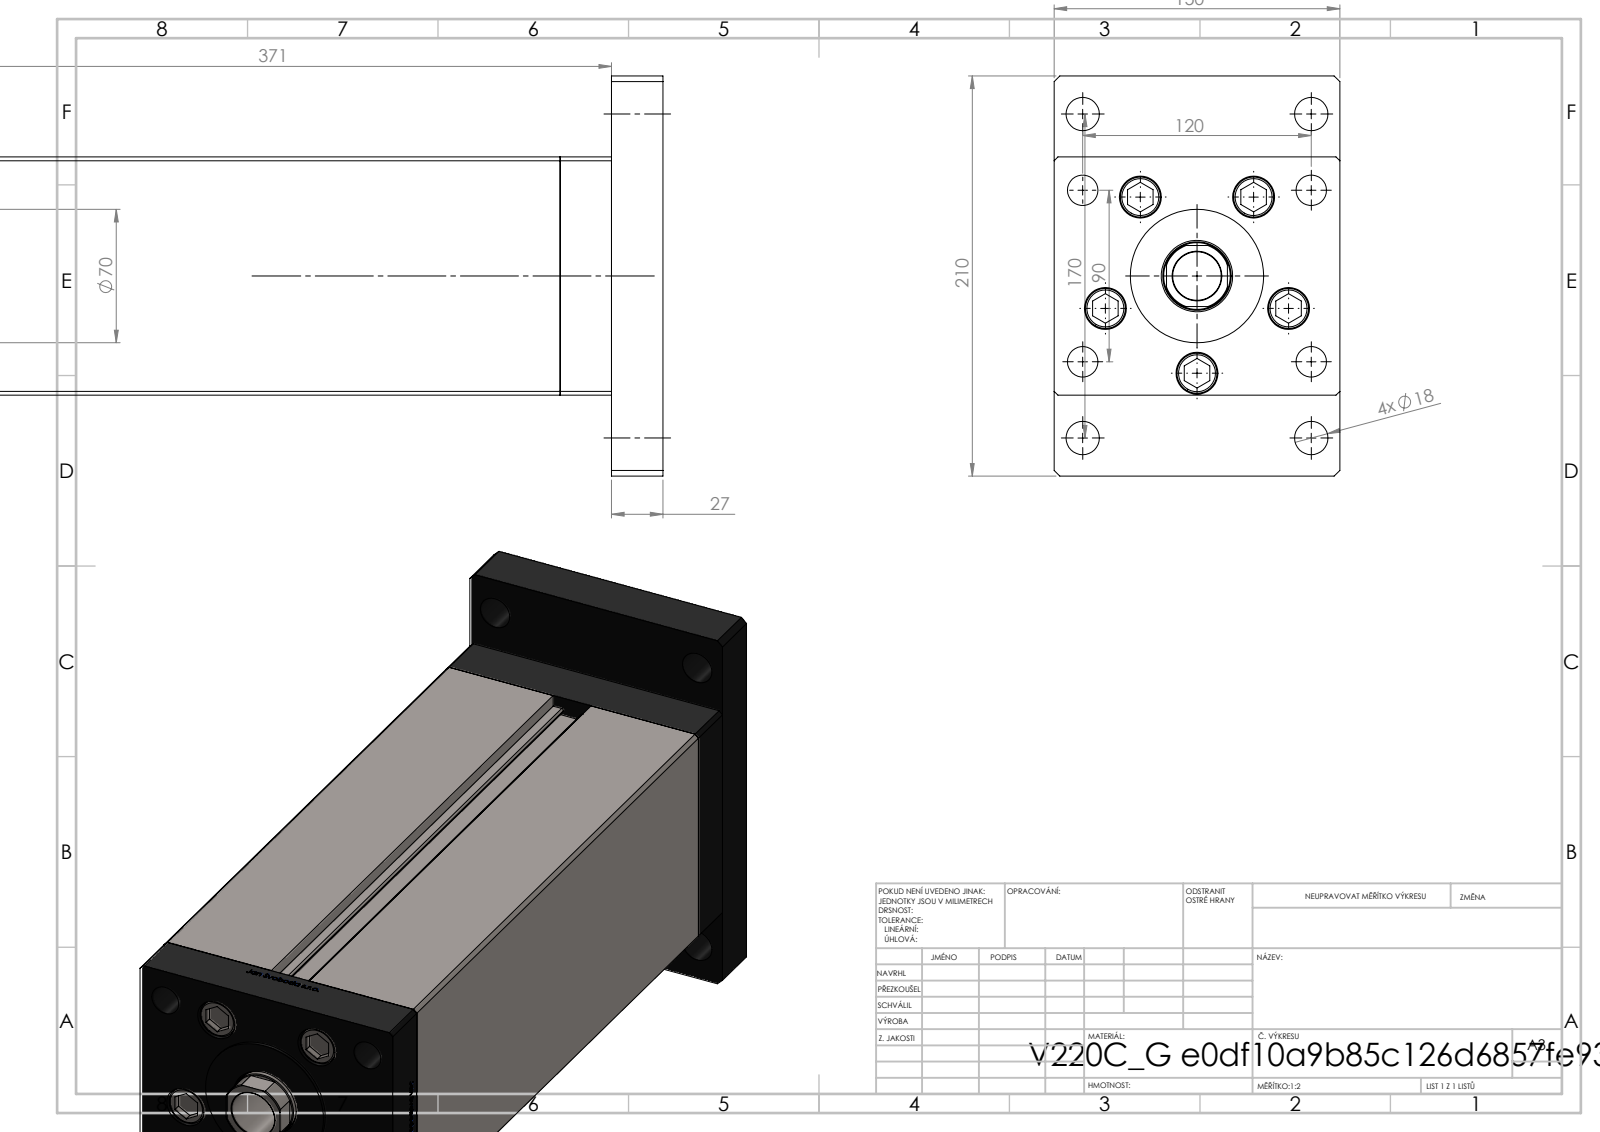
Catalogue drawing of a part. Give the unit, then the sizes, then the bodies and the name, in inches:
Units: inches
Overall size (bounding box): 16.26 × 8.268 × 5.906
Round holes (diameter × count): ⌀0.63 ×9, ⌀0.689 ×9, ⌀0.866 ×5, ⌀0.827 ×4, ⌀0.079 ×2, ⌀0.518 ×2, ⌀1.004 ×1, ⌀1.417 ×1, ⌀1.476 ×1, ⌀4.016 ×1
Round bosses / shafts (diameter × count): ⌀0.315 ×9, ⌀0.827 ×5, ⌀3.15 ×1, ⌀2.756 ×1
Partial cylindrical surfaces — rounded edges, fillets, slot ends (radius × count): R0.037 ×2, R0.689 ×1
Main face-to-face distances: 1.063, 5.906, 4.921, 13.543, 14.606, 12.48, 2.126, 0.079, 15.669, 14.528
Hole centre spacings: 2.008, 1.575, 2.953, 4.096, 4.724, 4.98, 5.118, 6.965
Volume: 397.7 in³ · Surface area: 942.6 in²
Bodies: 19 solids, 1313 faces (518 planar, 189 cylindrical, 606 other)
Part name (STEP PRODUCT): V220C_FRONT_G; V220C BACK_G; V220C_G_MIDDLE; ALLEN BOLT (+2 more)
STEP written by: SolidWorks 2019 (CONFIG_CONTROL_DESIGN)
